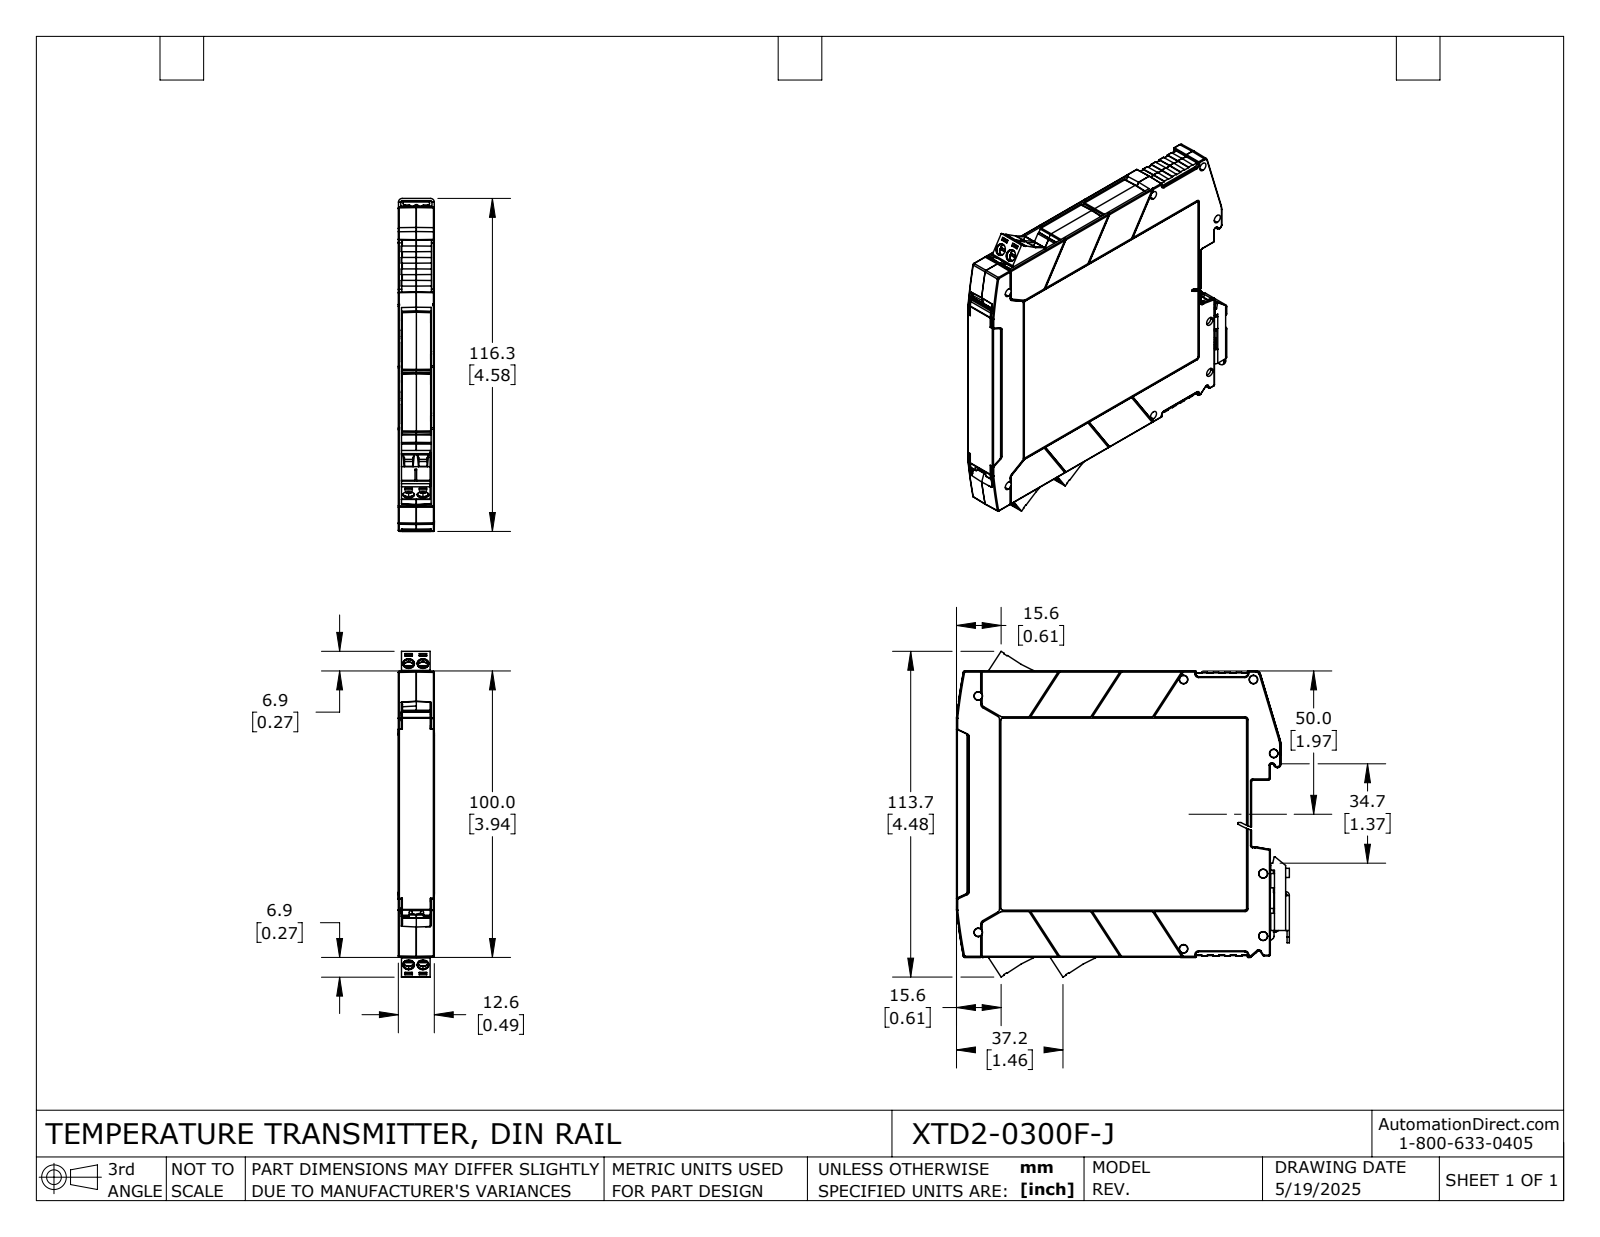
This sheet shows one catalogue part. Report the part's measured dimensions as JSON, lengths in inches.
{"part_name": "XTD2-0300F-J", "step_written_by": "SolidWorks 2024 (AUTOMOTIVE_DESIGN)", "units": "inches", "bodies": {"solids": 14, "faces": 3337, "planar": 1910, "cylindrical": 596, "other": 831}, "overall_size": [4.577, 4.478, 0.496], "volume_in3": 2.41, "surface_area_in2": 101.5, "round_holes": [[0.063, 6], [0.11, 6], [0.152, 6], [0.159, 6]], "round_bosses_or_shafts": [[0.156, 6], [0.098, 6], [0.059, 2], [0.053, 2]], "partial_cylinders_radius": [[0.008, 89], [0.012, 78], [0.02, 71], [0.039, 22], [0.004, 20], [0.016, 13], [0.006, 12], [0.028, 8]], "face_to_face_distances": [0.049, 0.445, 0.494, 0.396, 0.043, 0.451, 0.402, 0.031, 0.198, 0.247], "hole_center_spacings": [0.197, 0.464, 0.504, 0.713, 0.739]}
